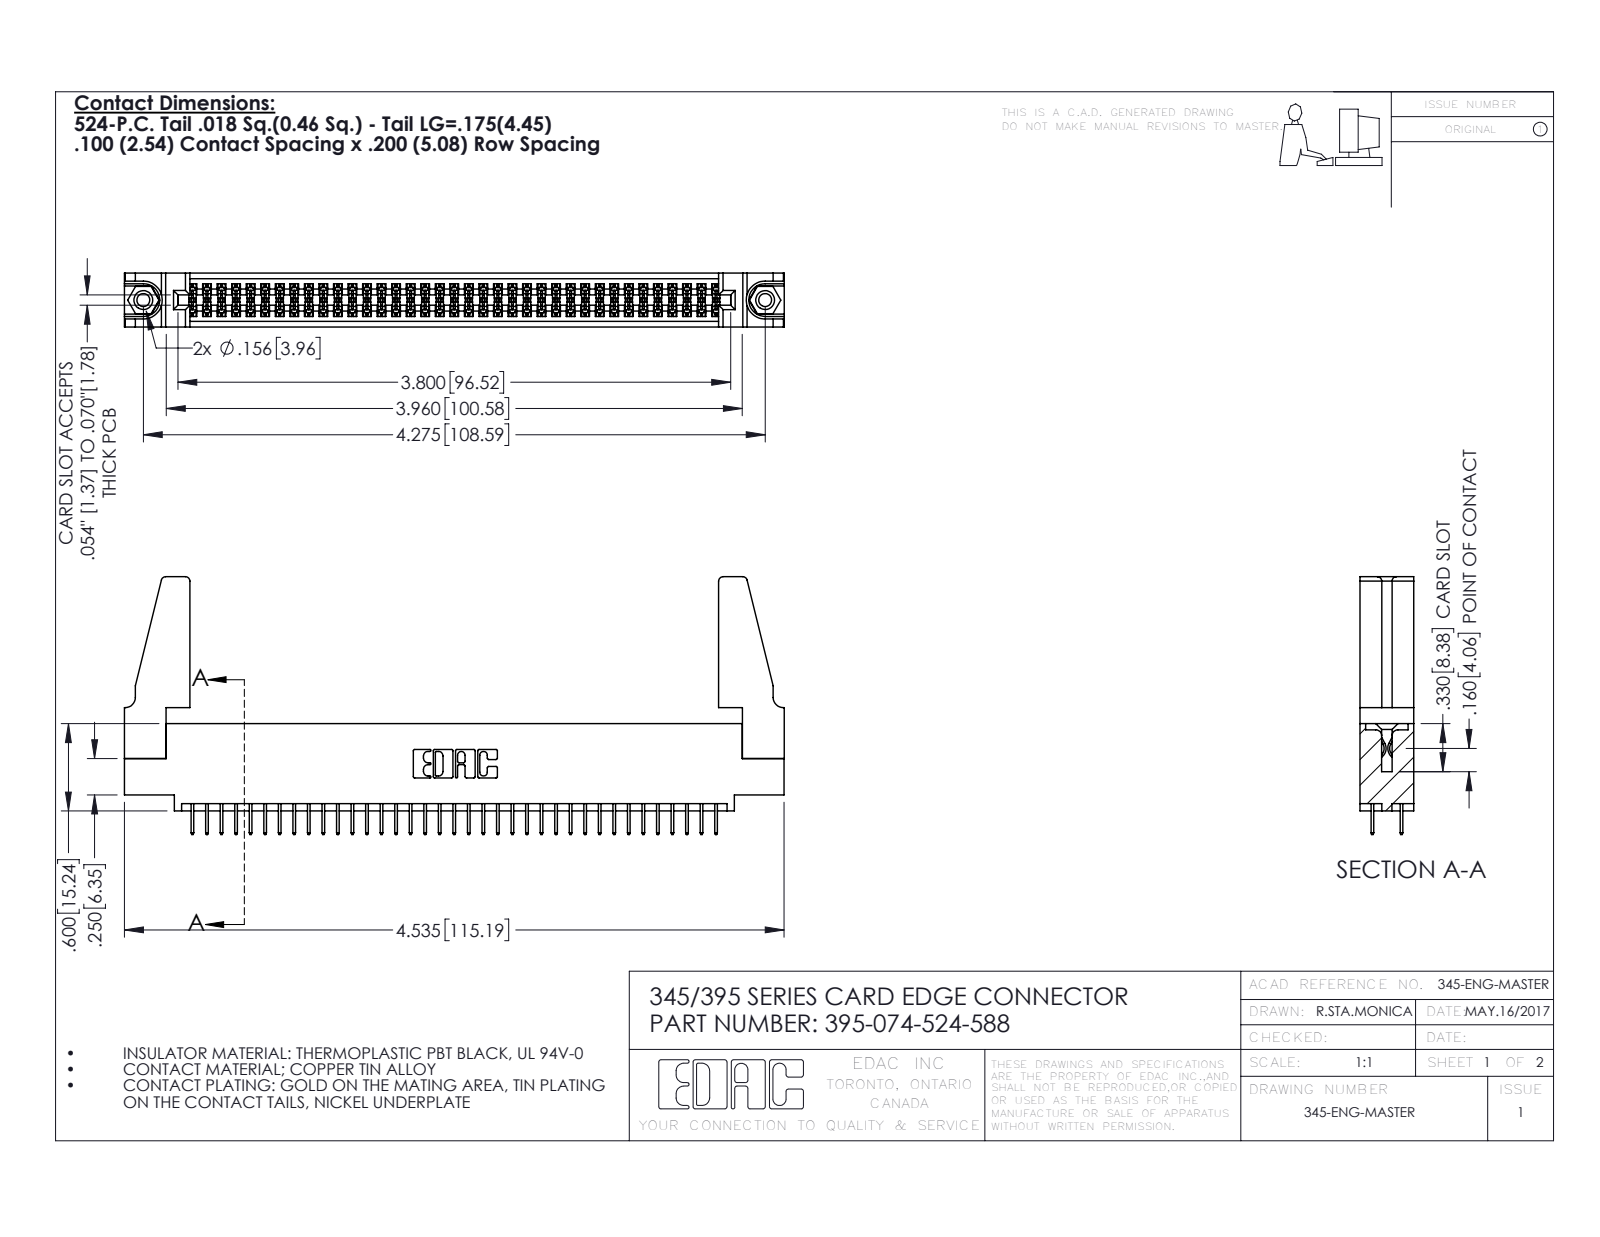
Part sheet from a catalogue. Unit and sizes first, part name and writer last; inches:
Units: inches
Overall size (bounding box): 4.536 × 1.772 × 0.37
Round holes (diameter × count): ⌀0.089 ×2, ⌀0.125 ×2, ⌀0.156 ×2, ⌀0.064 ×1
Round bosses / shafts (diameter × count): ⌀0.155 ×2
Partial cylindrical surfaces — rounded edges, fillets, slot ends (radius × count): R0.006 ×111, R0.01 ×22, R0.03 ×8, R0.007 ×6, R0.031 ×6, R0.026 ×3, R0.014 ×2, R0.019 ×2
Main face-to-face distances: 0.072, 0.298, 0.37, 0.2, 0.098, 0.272, 0.025, 0.225, 0.072, 0.175
Hole centre spacings: 0.27, 4.039, 4.275
Volume: 0.867 in³ · Surface area: 29.49 in²
Bodies: 79 solids, 4250 faces (3042 planar, 1192 cylindrical, 16 other)
Part name (STEP PRODUCT): 345-220-078_345-220-088; 395-074-524-588; 345-250-001_345-250-001-102; 345 Part_0.110 Offset - 0.156 Dia-TH (+1 more)
STEP written by: SolidWorks 2016 (CONFIG_CONTROL_DESIGN)
